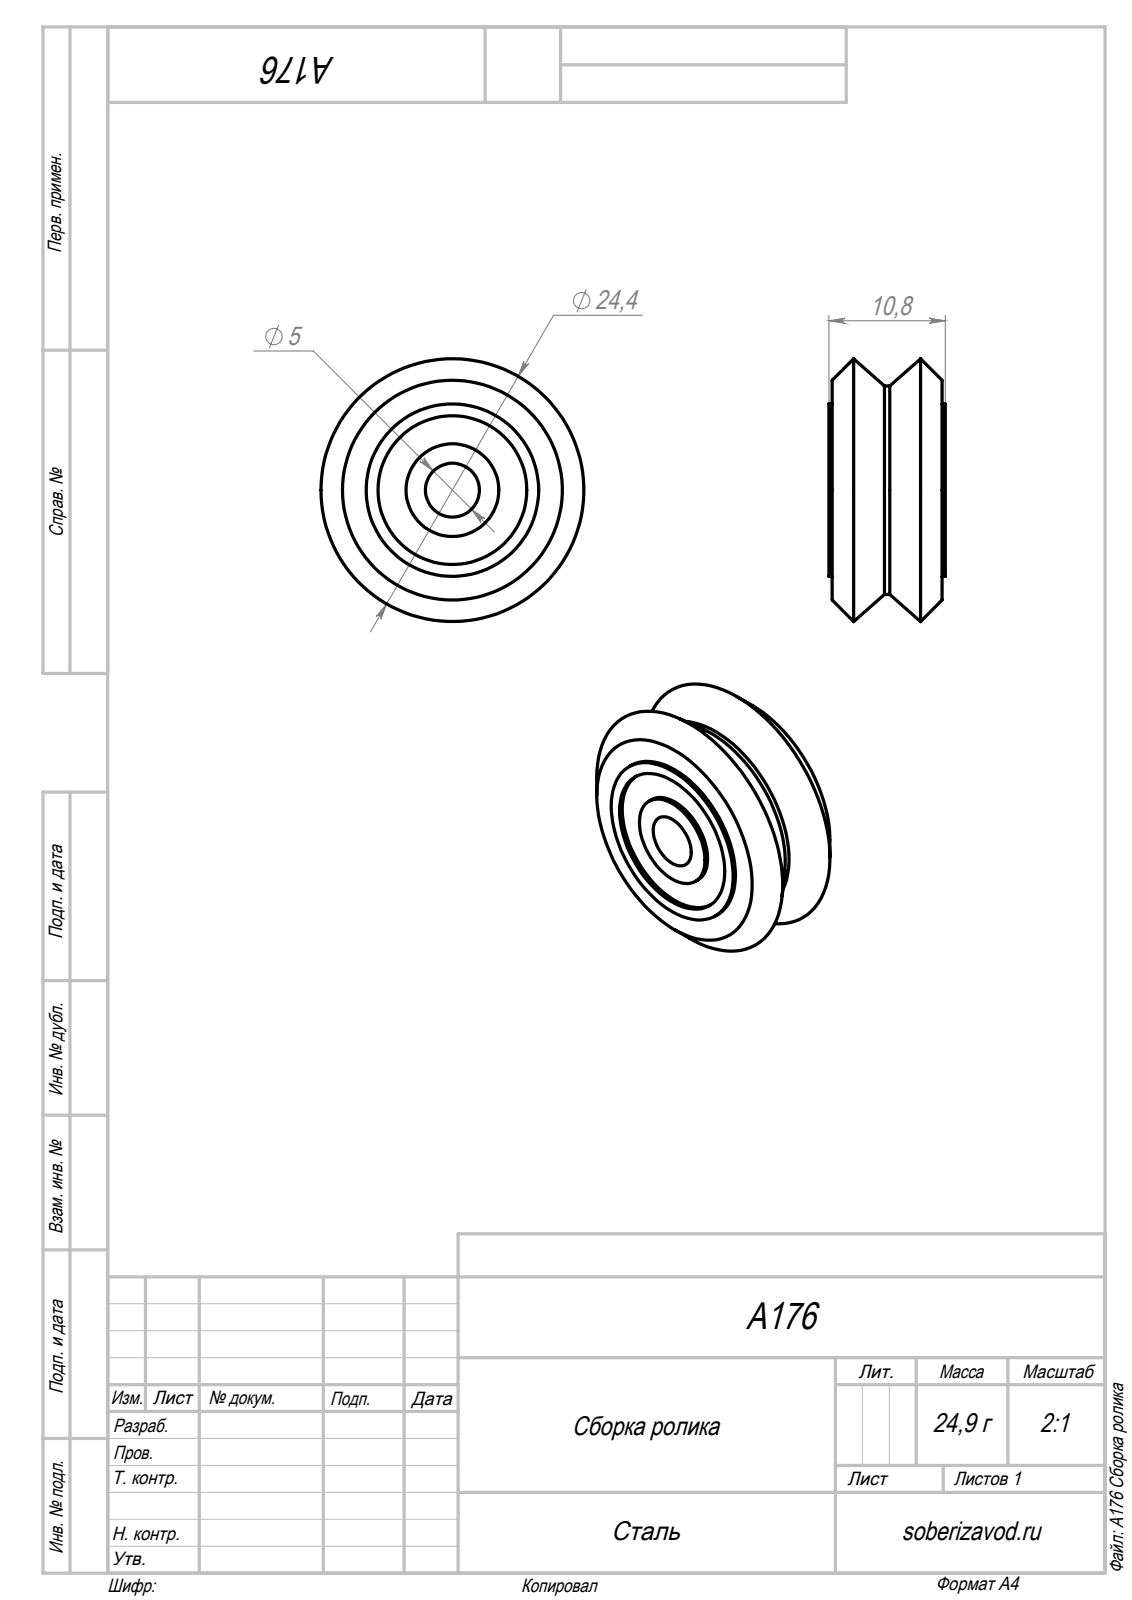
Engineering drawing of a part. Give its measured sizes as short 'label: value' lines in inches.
name: A180 Подшипник 625rs, O 5 O 16; A211 Высокоточная дистанционная шайба 5 мм_00; A176 Сборка ролика
written by: SolidWorks 2018 (AUTOMOTIVE_DESIGN)
unit: in
bodies: 4 solids, 62 faces (18 planar, 36 cylindrical, 8 other)
size: 0.96 × 0.96 × 0.425
volume: 0.22 in³; area: 5.348 in²
holes: 1× ⌀0.197, 1× ⌀0.205, 1× ⌀0.543, 1× ⌀0.551, 1× ⌀0.63
bosses: 1× ⌀0.762, 1× ⌀0.394, 1× ⌀0.339
face distances: 0.014, 0.183, 0.228, 0.185, 0.217, 0.171, 0.23, 0.4, 0.169, 0.215
